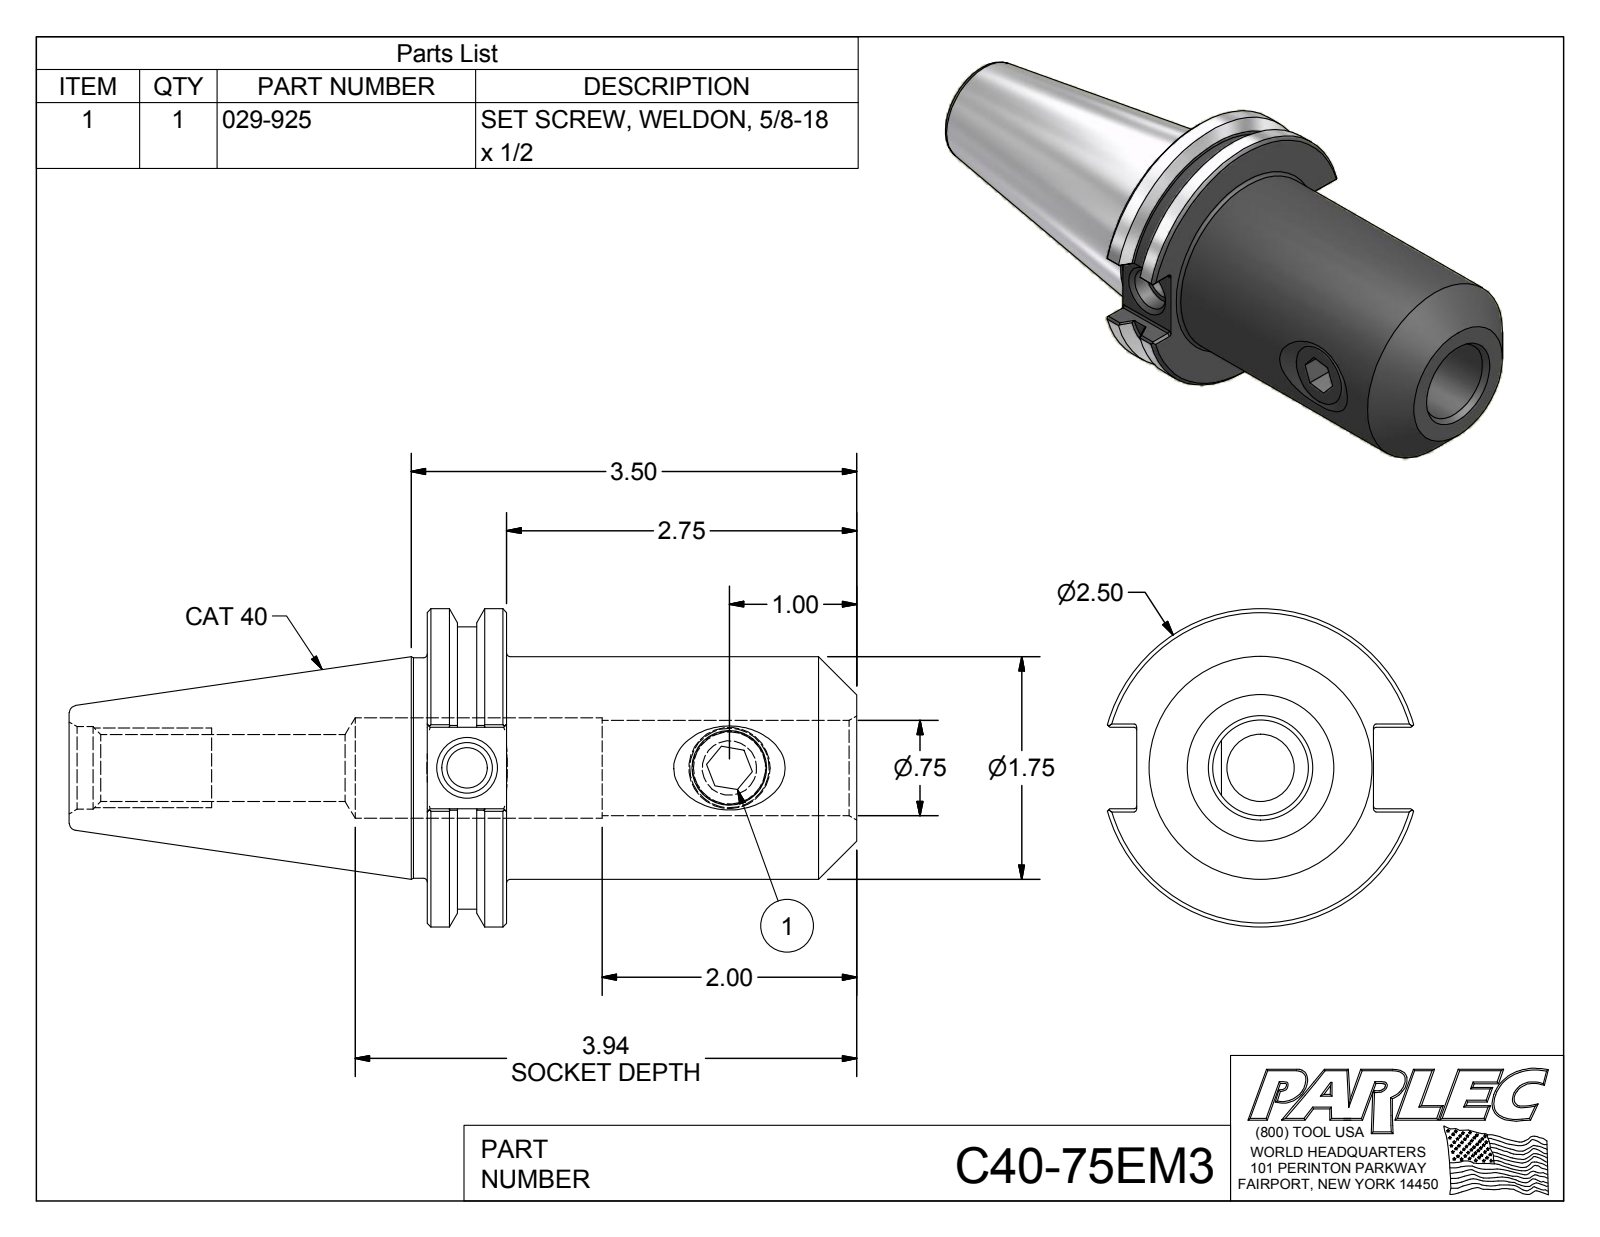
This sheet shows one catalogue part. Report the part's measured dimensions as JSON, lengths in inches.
{"part_name": "C40-75EM3; C40-75EM3-1; 029-925", "step_written_by": "Autodesk Inventor 2012 (AUTOMOTIVE_DESIGN)", "units": "inches", "bodies": {"solids": 2, "faces": 102, "planar": 41, "cylindrical": 29, "other": 32}, "overall_size": [6.187, 2.5, 2.406], "volume_in3": 10.84, "surface_area_in2": 55.33, "round_holes": [[0.315, 1], [0.399, 1], [0.527, 1], [0.578, 1], [0.648, 1], [0.75, 1], [0.79, 1]], "round_bosses_or_shafts": [[2.5, 1], [2.219, 1], [1.75, 1], [1.73, 1], [0.625, 1]], "partial_cylinders_radius": [[0.02, 12]], "face_to_face_distances": [0.625, 3.375, 2.75, 0.64, 0.315, 1.86, 2.812, 3.437, 6.187, 1.693], "hole_center_spacings": [2.06]}
